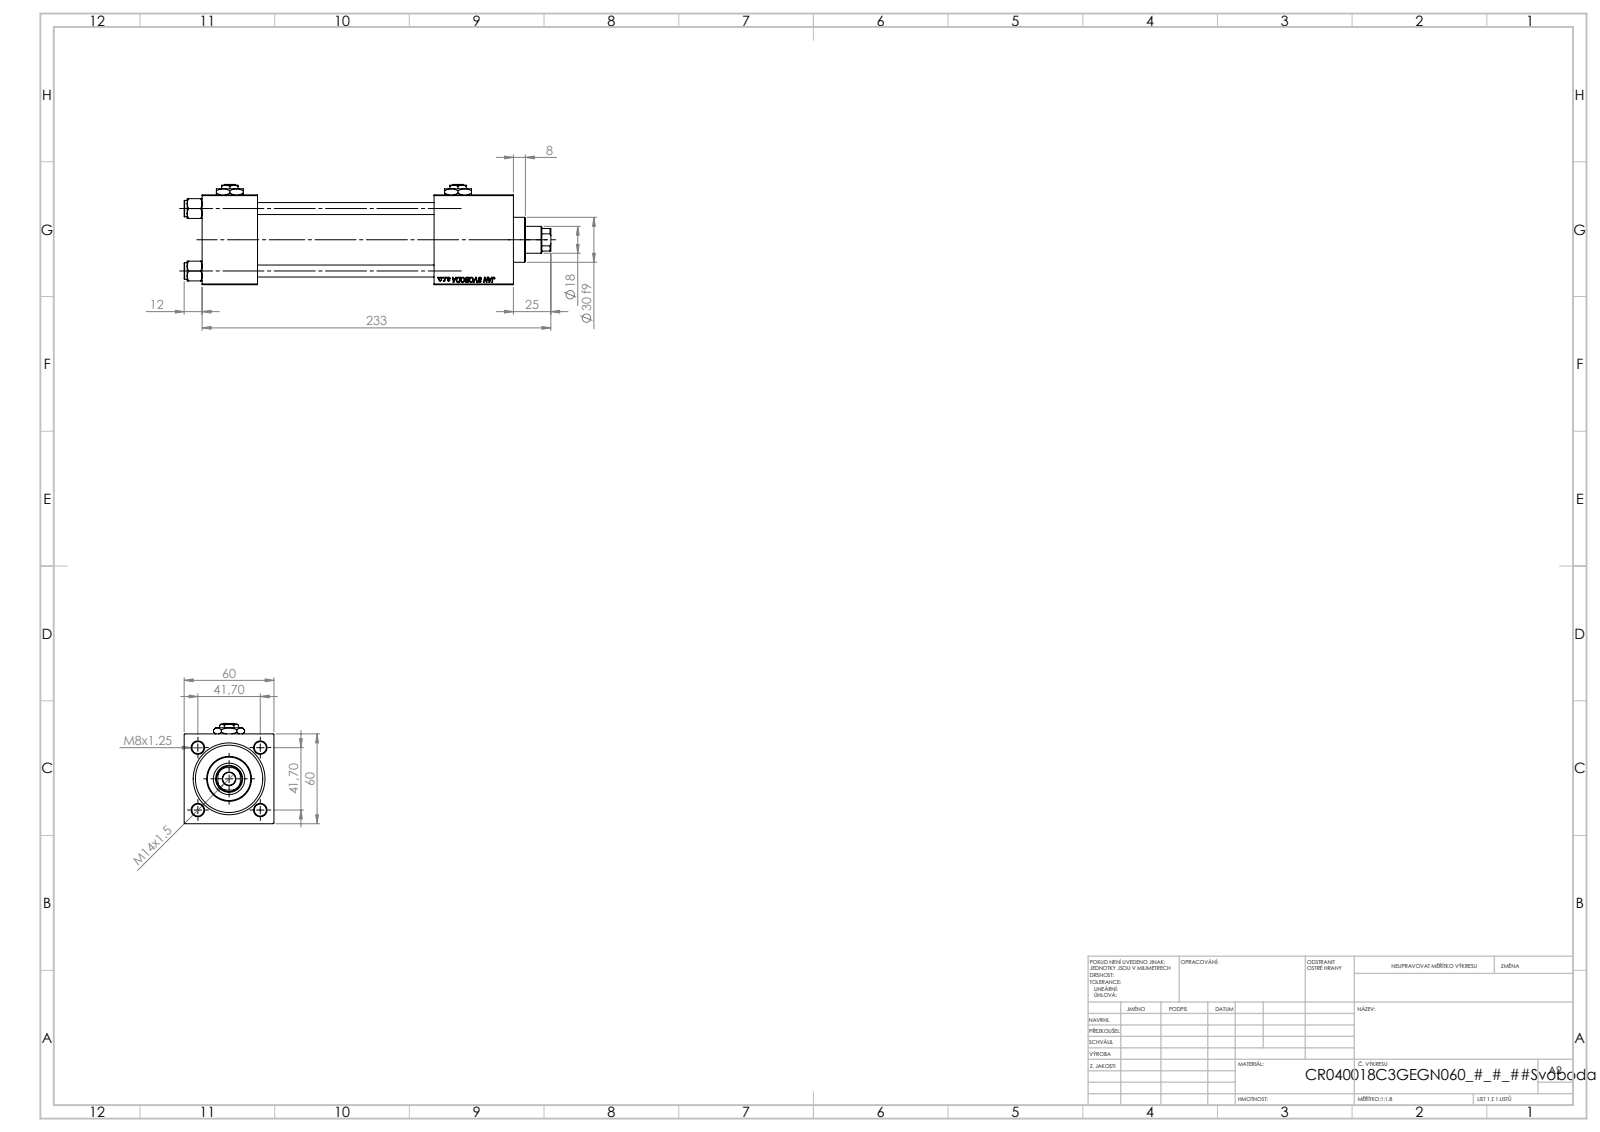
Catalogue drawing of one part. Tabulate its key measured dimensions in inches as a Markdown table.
| quantity | value |
| --- | --- |
| part name | V215CR_VCP_C; V215CR_C_Body; Zatka_pro_OIL_PORT; NUT_M5_C (+2 more) |
| STEP written by | SolidWorks 2019 (CONFIG_CONTROL_DESIGN) |
| units | inches |
| bodies | 13 solids, 1250 faces (574 planar, 98 cylindrical, 578 other) |
| overall size | 9.646 × 2.638 × 2.362 |
| volume | 27.49 in³ |
| surface area | 207.7 in² |
| round holes (diameter × count) | 0.315 × 4, 0.276 × 2, 0.656 × 2, 0.945 × 2, 0.335 × 1, 0.709 × 1, 0.827 × 1, 1.22 × 1, 1.575 × 1, 1.772 × 1 |
| round bosses / shafts (diameter × count) | 0.433 × 4, 1.811 × 1, 1.181 × 1 |
| partial cylindrical surfaces (radius × count) | 0.335 × 1 |
| main face-to-face distances | 2.362, 1.457, 8.189, 6.732, 2.087, 6.102, 4.646, 7.059, 5.602, 0.957 |
| hole center spacings | 1.161, 1.642, 2.322, 6.004 |
